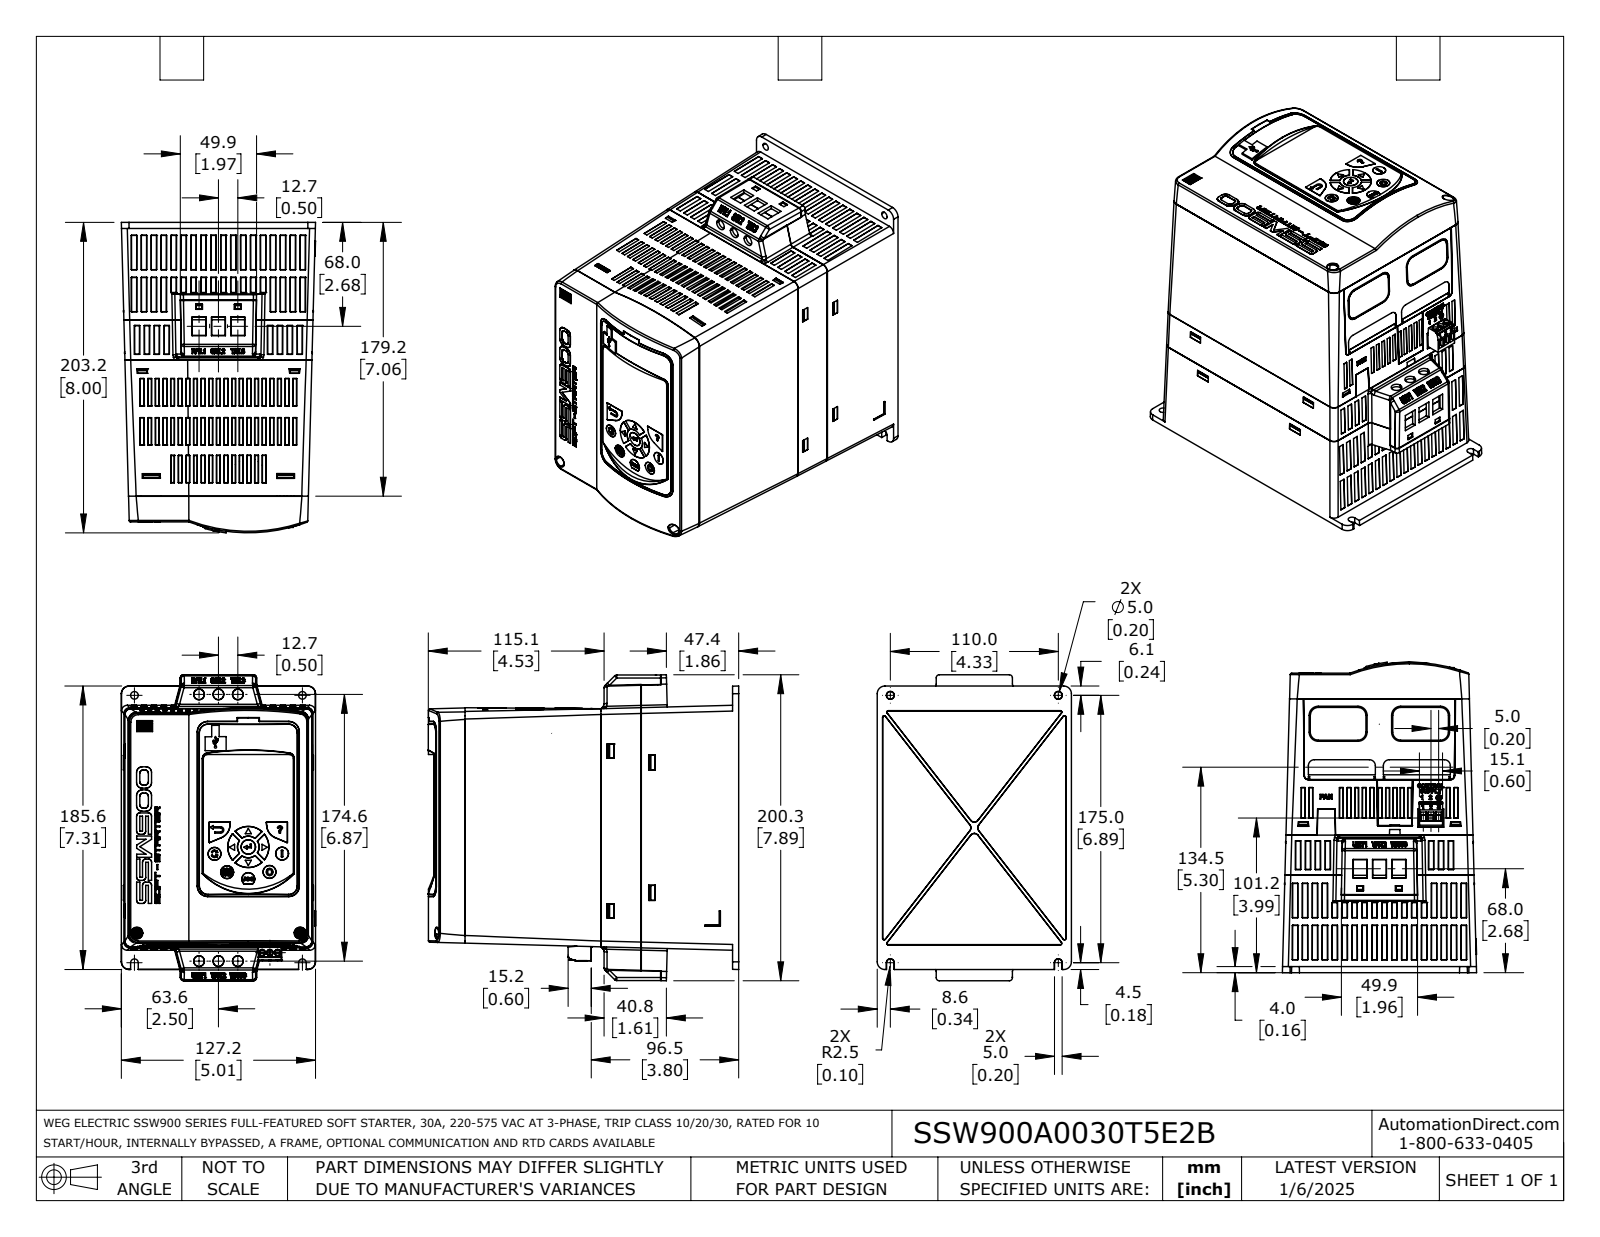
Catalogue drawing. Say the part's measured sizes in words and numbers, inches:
The part is named "SSW900A0030T5E2B". Its 3-D file was written by "SolidWorks 2021 (AUTOMOTIVE_DESIGN)". It is 3 solids with 4554 faces: 3611 planar, 239 cylindrical and 704 other. Overall it measures 8.002 by 7.885 by 5.006 inches. Its volume is 41.94 cubic inches and its surface area 551 square inches. Round holes: 3 of diameter 0.118, 3 of diameter 0.165, 1 of diameter 0.133, 1 of diameter 0.287. Round bosses or shafts: 3 of diameter 0.15, 2 of diameter 0.087, 1 of diameter 0.151, 1 of diameter 0.057, 1 of diameter 0.034. Partial cylindrical surfaces (rounded edges, fillets, slot ends): 42 of radius 0.079, 19 of radius 0.02, 17 of radius 0.039, 14 of radius 0.012, 8 of radius 0.008, 8 of radius 0.15, 8 of radius 0.157, 7 of radius 0.006. The main face-to-face distances are 4.466, 0.325, 5.776, 0.15, 0.149, 0.149, 7.811, 7.487, 0.055, 0.333. The hole center spacings are 0.197, 0.199, 0.394, 0.398, 0.565, 0.601, 0.693, 0.768.
